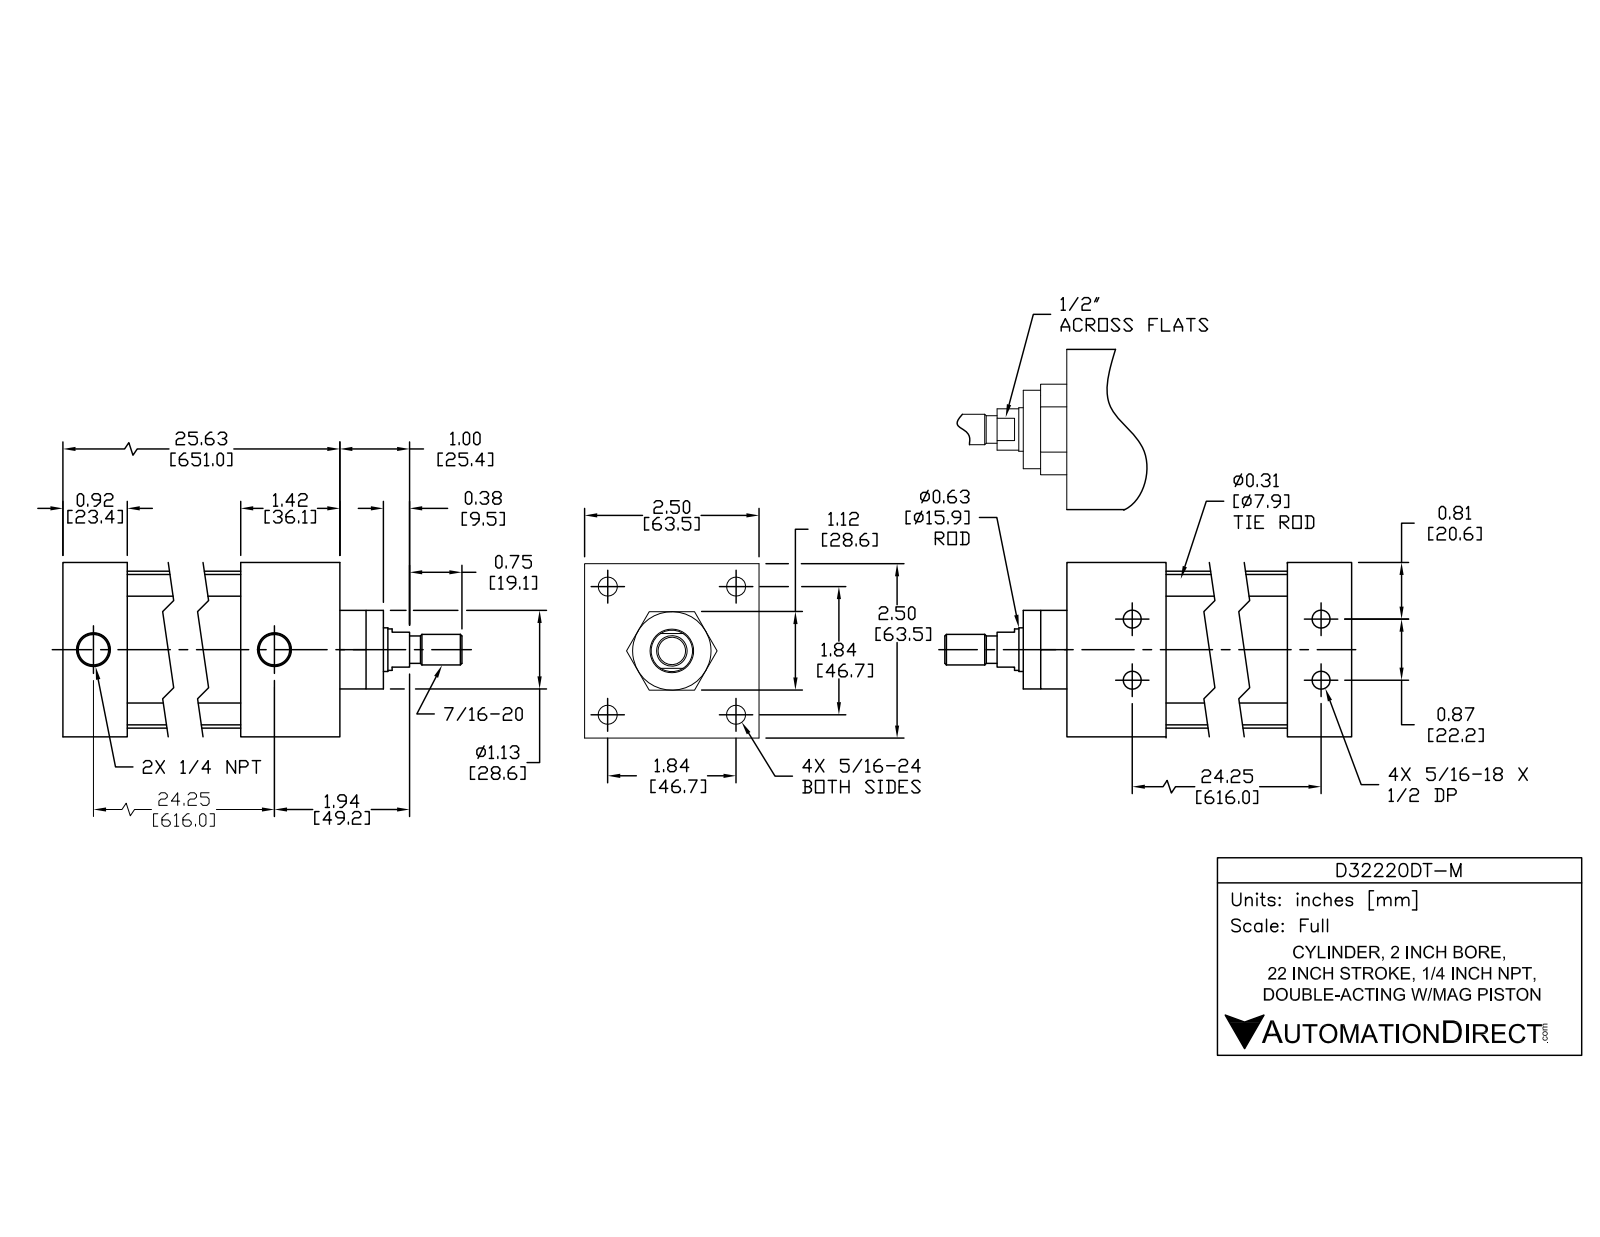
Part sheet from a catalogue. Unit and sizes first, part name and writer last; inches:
Units: inches
Overall size (bounding box): 27.371 × 2.5 × 2.5
Round holes (diameter × count): ⌀0.252 ×4, ⌀0.267 ×4, ⌀0.359 ×4, ⌀0.5 ×4, ⌀0.297 ×2, ⌀0.477 ×2, ⌀0.625 ×1, ⌀0.628 ×1, ⌀2 ×1
Round bosses / shafts (diameter × count): ⌀0.484 ×4, ⌀0.313 ×4, ⌀0.282 ×4, ⌀2.25 ×1, ⌀1.997 ×1, ⌀1.12 ×1, ⌀0.622 ×1, ⌀0.59 ×1
Partial cylindrical surfaces — rounded edges, fillets, slot ends (radius × count): R0.25 ×4
Main face-to-face distances: 2.5, 0.08, 23.201, 25.621, 1.42, 24.201, 23.281, 24.701, 0.92, 1
Hole centre spacings: 1.307, 1.848, 24.249, 24.245, 0.437, 0.438, 0.875, 2.613
Volume: 50.38 in³ · Surface area: 538.2 in²
Bodies: 12 solids, 298 faces (94 planar, 114 cylindrical, 90 other)
Part name (STEP PRODUCT): D32220DT-M PISTON; D32220DT-M; D32220DT-M BODY
STEP written by: SolidWorks 2015 (AUTOMOTIVE_DESIGN)
